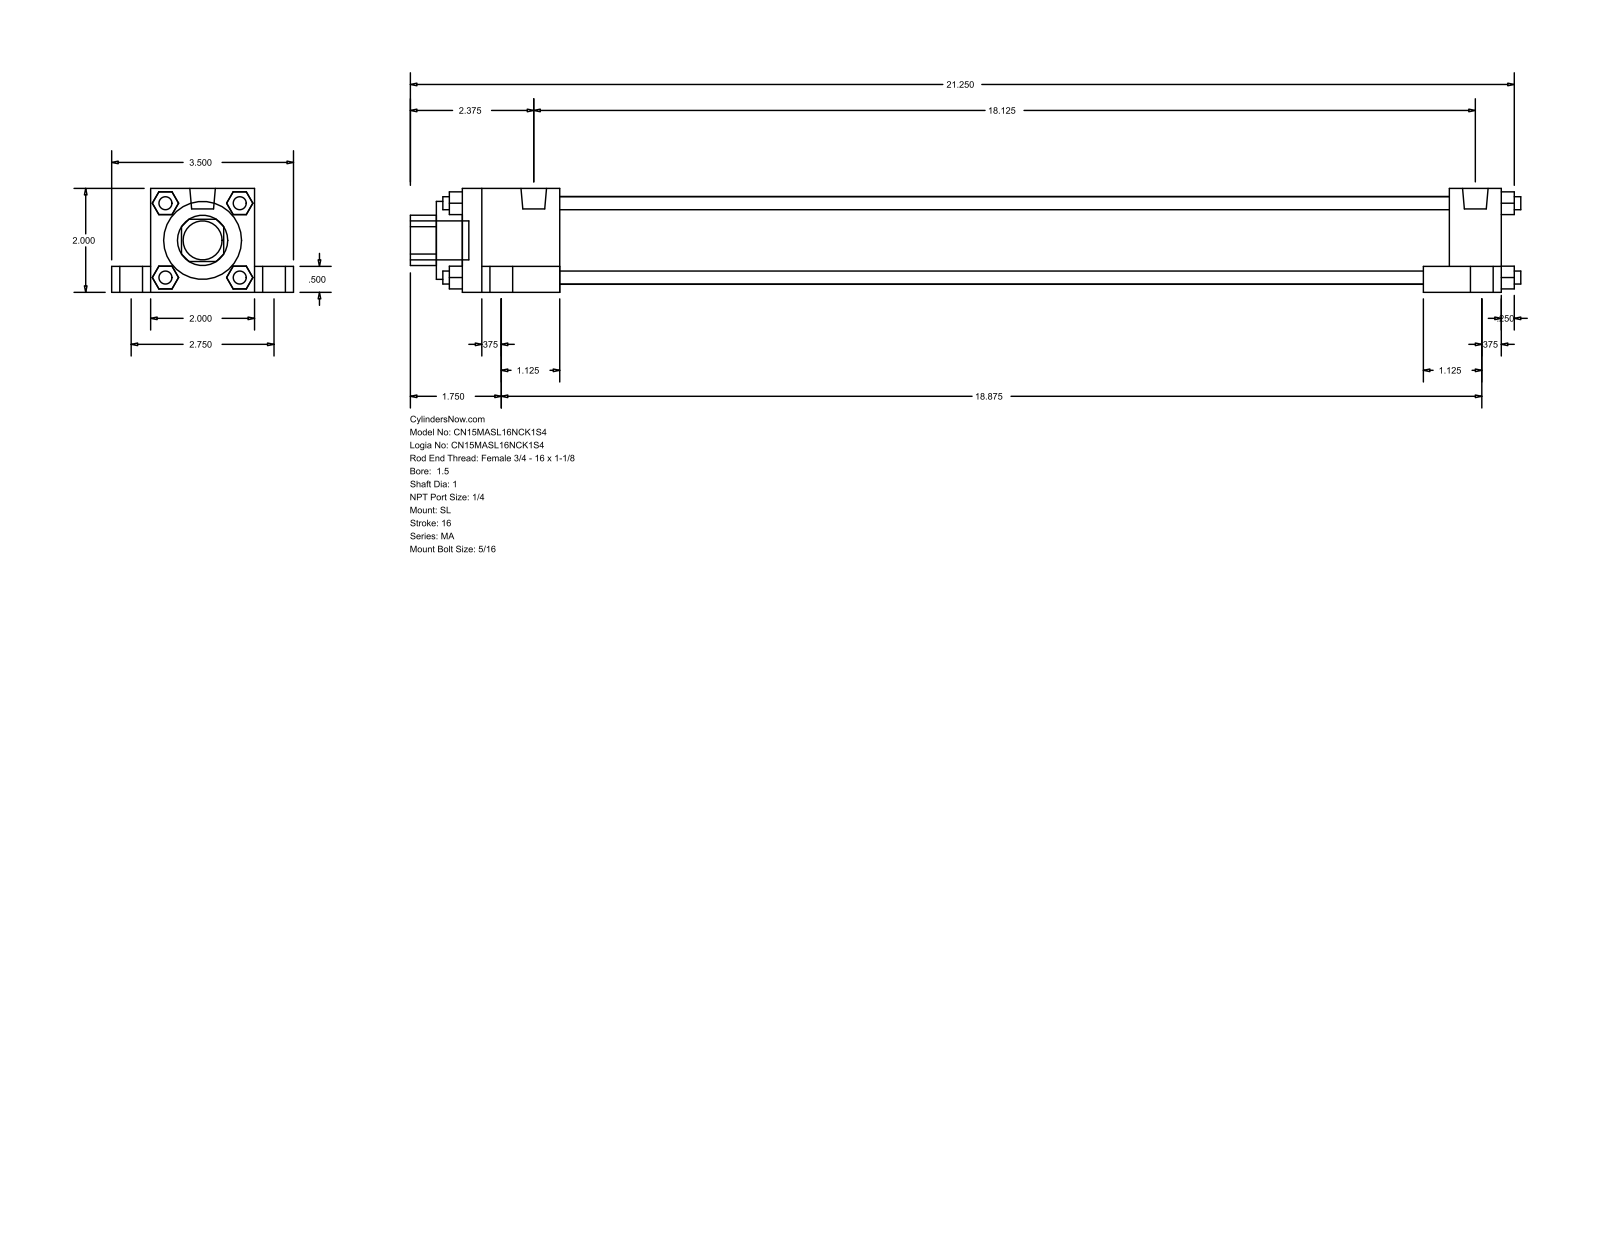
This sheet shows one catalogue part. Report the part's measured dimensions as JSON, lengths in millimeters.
{"part_name": "MA_SL__0150_1", "step_written_by": "GSSL Pune (CONFIG_CONTROL_DESIGN)", "units": "millimeters", "bodies": {"solids": 0, "faces": 148, "planar": 112, "cylindrical": 36, "other": 0}, "overall_size": [542.92, 88.9, 50.8], "round_holes": [[25.4, 1], [38.1, 1], [42.93, 1]], "round_bosses_or_shafts": [[17.46, 4], [11.11, 4], [7.94, 4], [6.35, 4], [12.49, 2], [19.05, 1]], "partial_cylinders_radius": [[12.29, 1]], "face_to_face_distances": [50.8, 12.7, 19.05, 9.52, 69.85, 38.1, 6.35, 508, 25.4, 482.6]}
